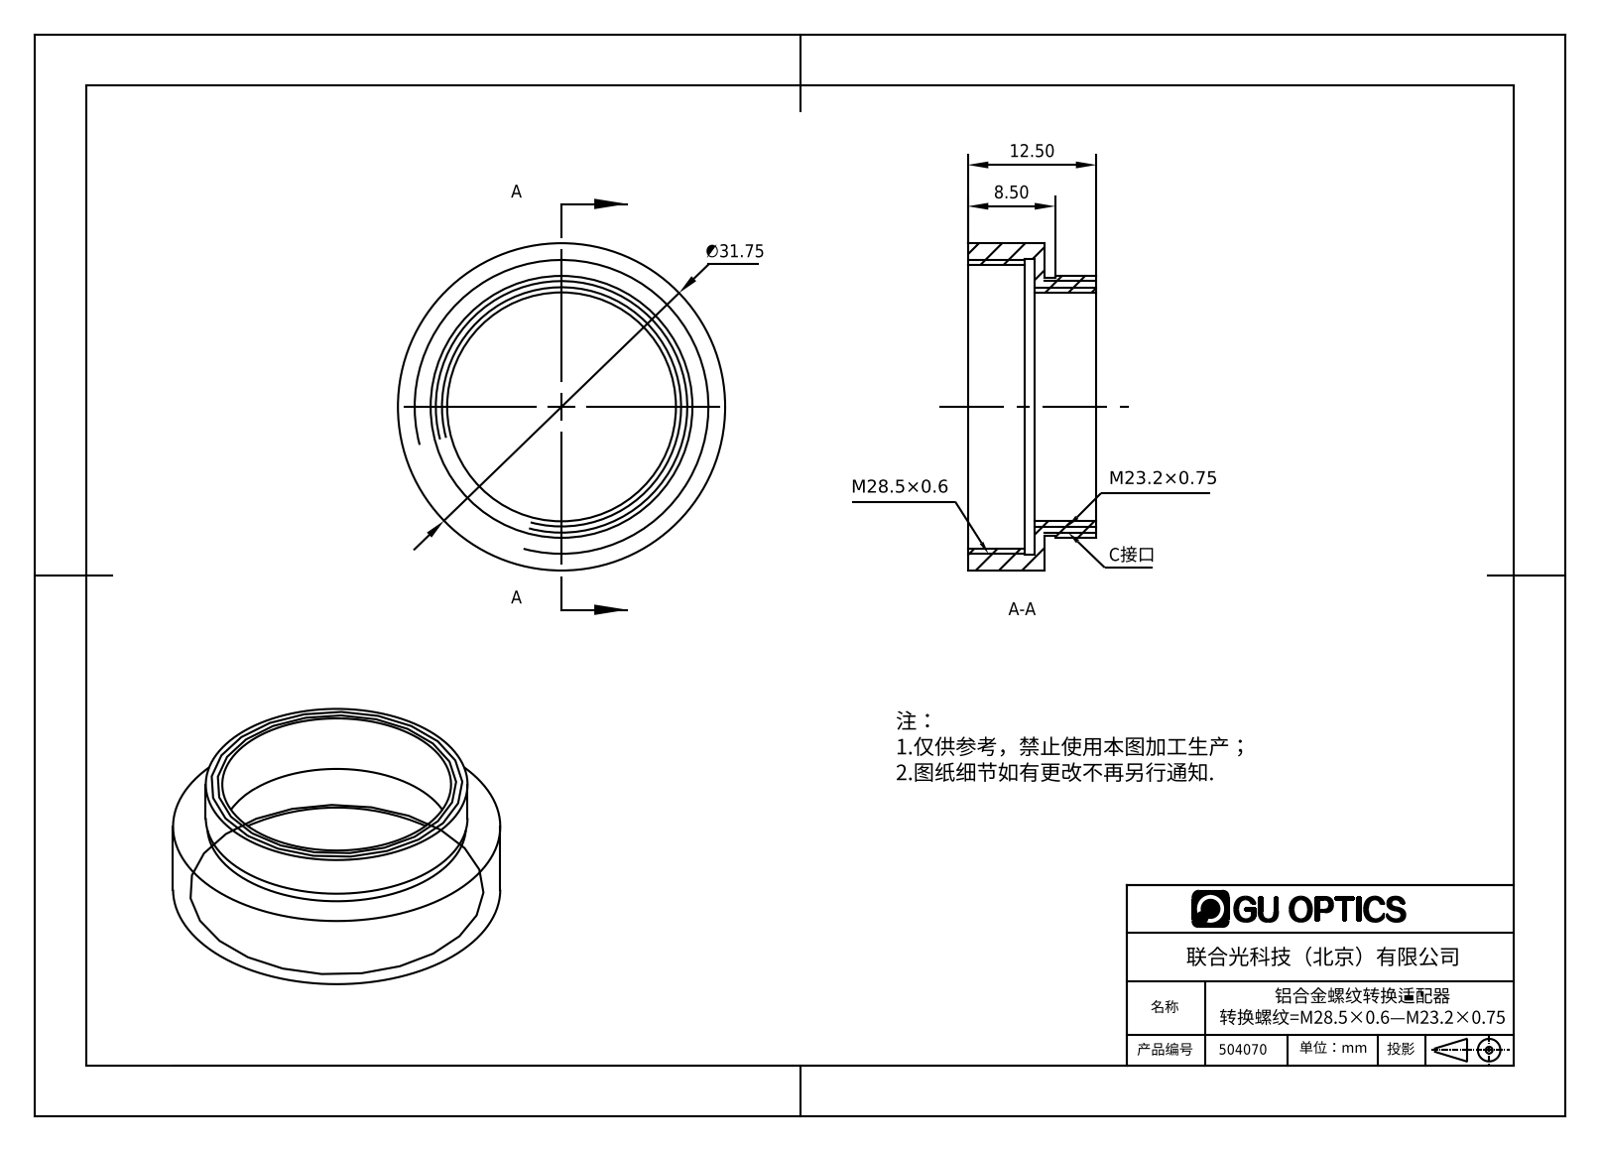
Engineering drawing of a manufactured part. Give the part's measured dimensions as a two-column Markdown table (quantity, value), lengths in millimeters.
| quantity | value |
| --- | --- |
| part name | 504070 |
| STEP written by | SolidWorks 2016 (AUTOMOTIVE_DESIGN) |
| units | millimeters |
| bodies | 1 solid, 18 faces (6 planar, 12 cylindrical, 0 other) |
| overall size | 31.75 × 31.75 × 12.5 |
| volume | 2 419 mm³ |
| surface area | 3 193 mm² |
| round holes (diameter × count) | 19 × 1, 27.5 × 1, 28.7 × 1 |
| round bosses / shafts (diameter × count) | 31.75 × 1, 23.2 × 1, 22.7 × 1 |
| main face-to-face distances | 1, 6.5, 7.5, 12.5, 6, 5, 2, 5.5, 7, 8.5 |
